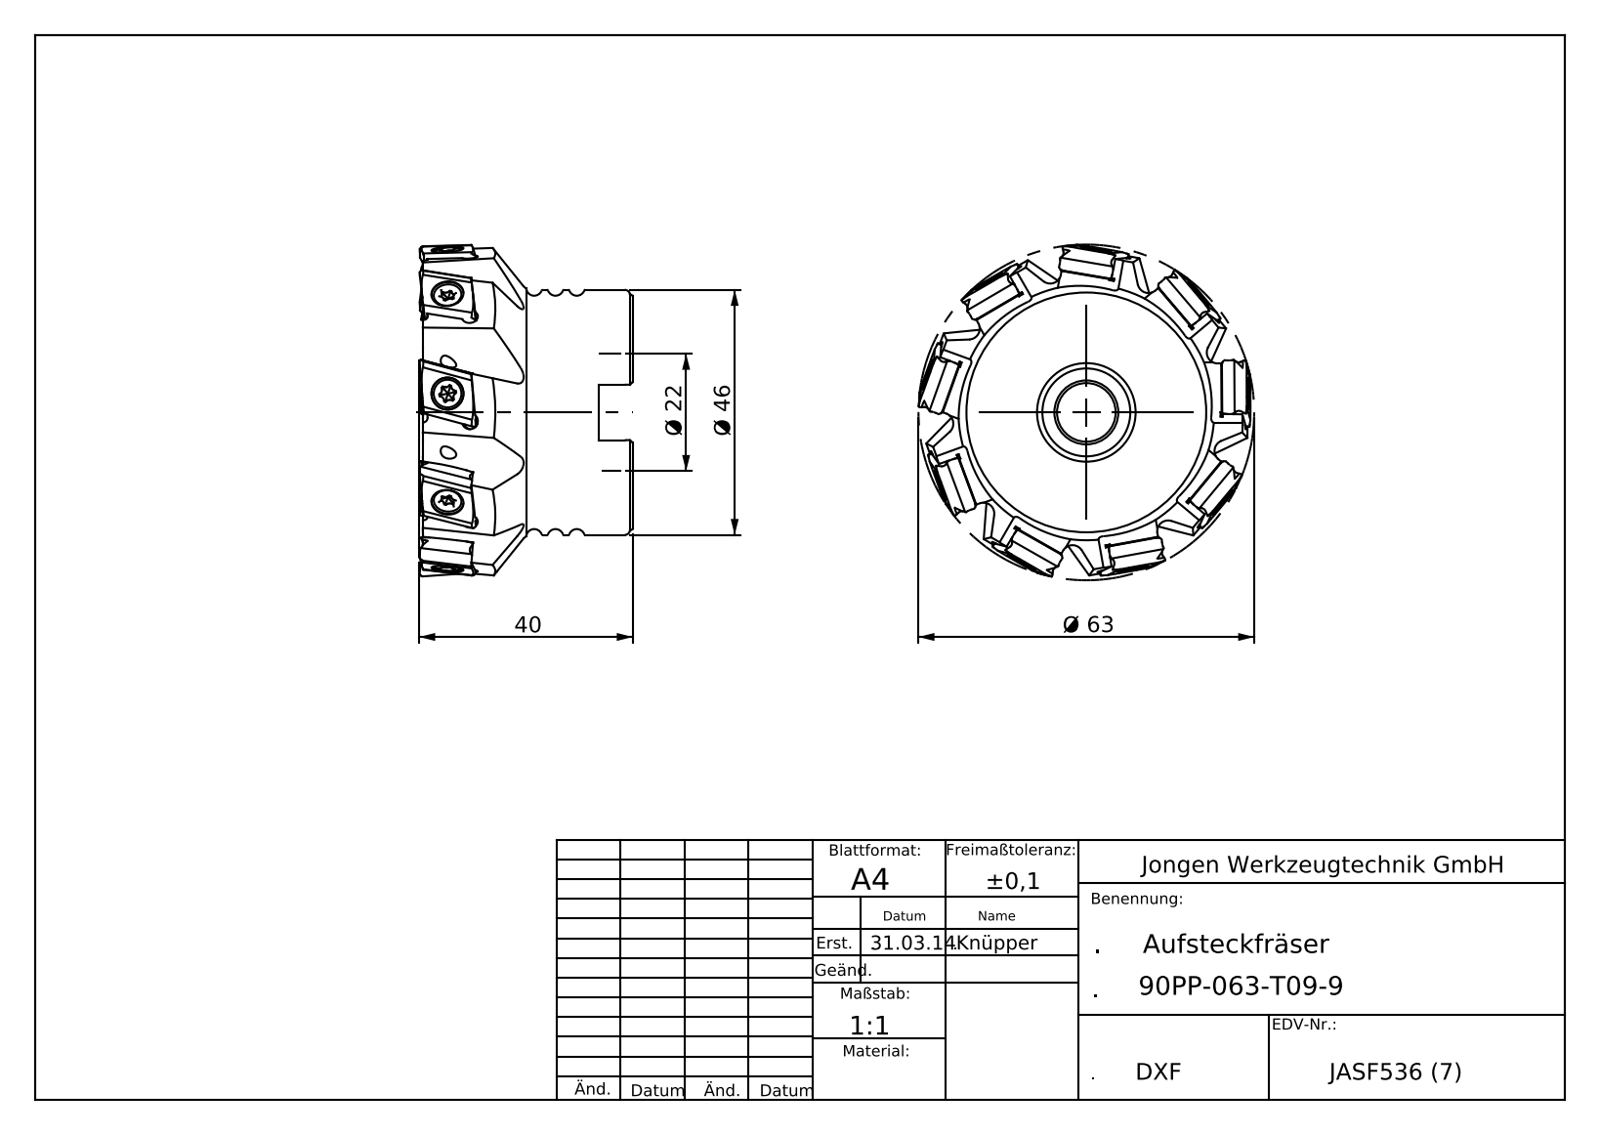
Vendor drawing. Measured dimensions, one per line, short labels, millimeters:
name: 90PP_063_T09_9
written by: SolidWorks 2015 (AUTOMOTIVE_DESIGN)
unit: mm
bodies: 1 solid, 239 faces (114 planar, 80 cylindrical, 45 other)
size: 63 × 63 × 40.1
volume: 66 828 mm³; area: 17 859 mm²
holes: 9× ⌀2.1, 9× ⌀3.3, 1× ⌀11, 1× ⌀16.5, 1× ⌀22, 1× ⌀22.15, 1× ⌀22.3
bosses: 1× ⌀46
rounds: 9× R0.9, 9× R1.5, 9× R2, 1× R23.25
face distances: 36.9, 20, 16.9, 6.3, 13.7, 30.6, 10.4, 39.4, 33.1, 19.4
